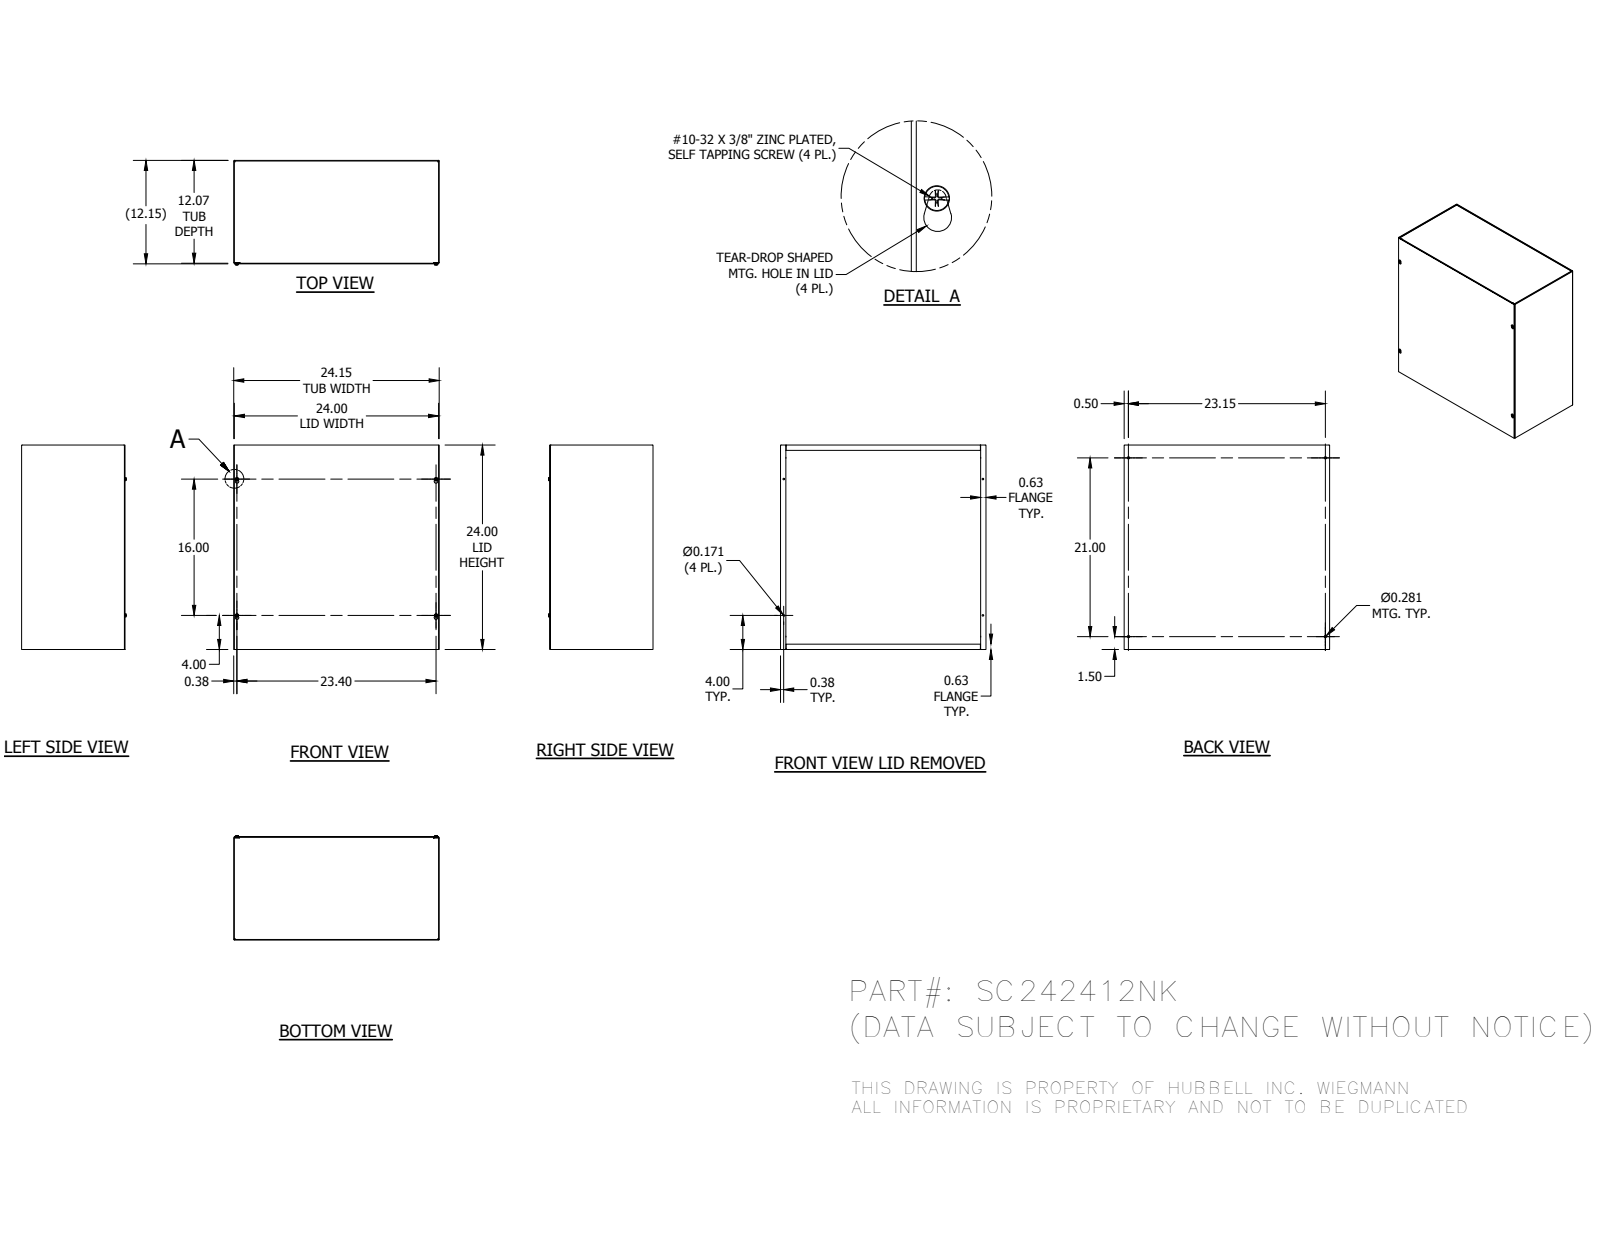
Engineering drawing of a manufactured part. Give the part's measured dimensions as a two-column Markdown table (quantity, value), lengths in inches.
| quantity | value |
| --- | --- |
| part name | SC242412NKBLR; SC2412NKTB; SC2424LPA; 37214 (+1 more) |
| STEP written by | Autodesk Inventor 2014 (AUTOMOTIVE_DESIGN) |
| units | inches |
| bodies | 8 solids, 320 faces (192 planar, 44 cylindrical, 84 other) |
| overall size | 24.148 × 24 × 12.28 |
| volume | 178.1 in³ |
| surface area | 4 842 in² |
| round holes (diameter × count) | 0.171 × 4, 0.281 × 4 |
| round bosses / shafts (diameter × count) | 0.19 × 4 |
| partial cylindrical surfaces (radius × count) | 0.016 × 12, 0.09 × 12, 0.125 × 4, 0.203 × 4 |
| main face-to-face distances | 0.074, 12.074, 12, 24, 23.926, 12.148, 24.074, 23.852, 24.148, 0.148 |
| hole center spacings | 2.503, 18.5, 23.407, 29.73, 16, 21, 23.148, 23.398 |
